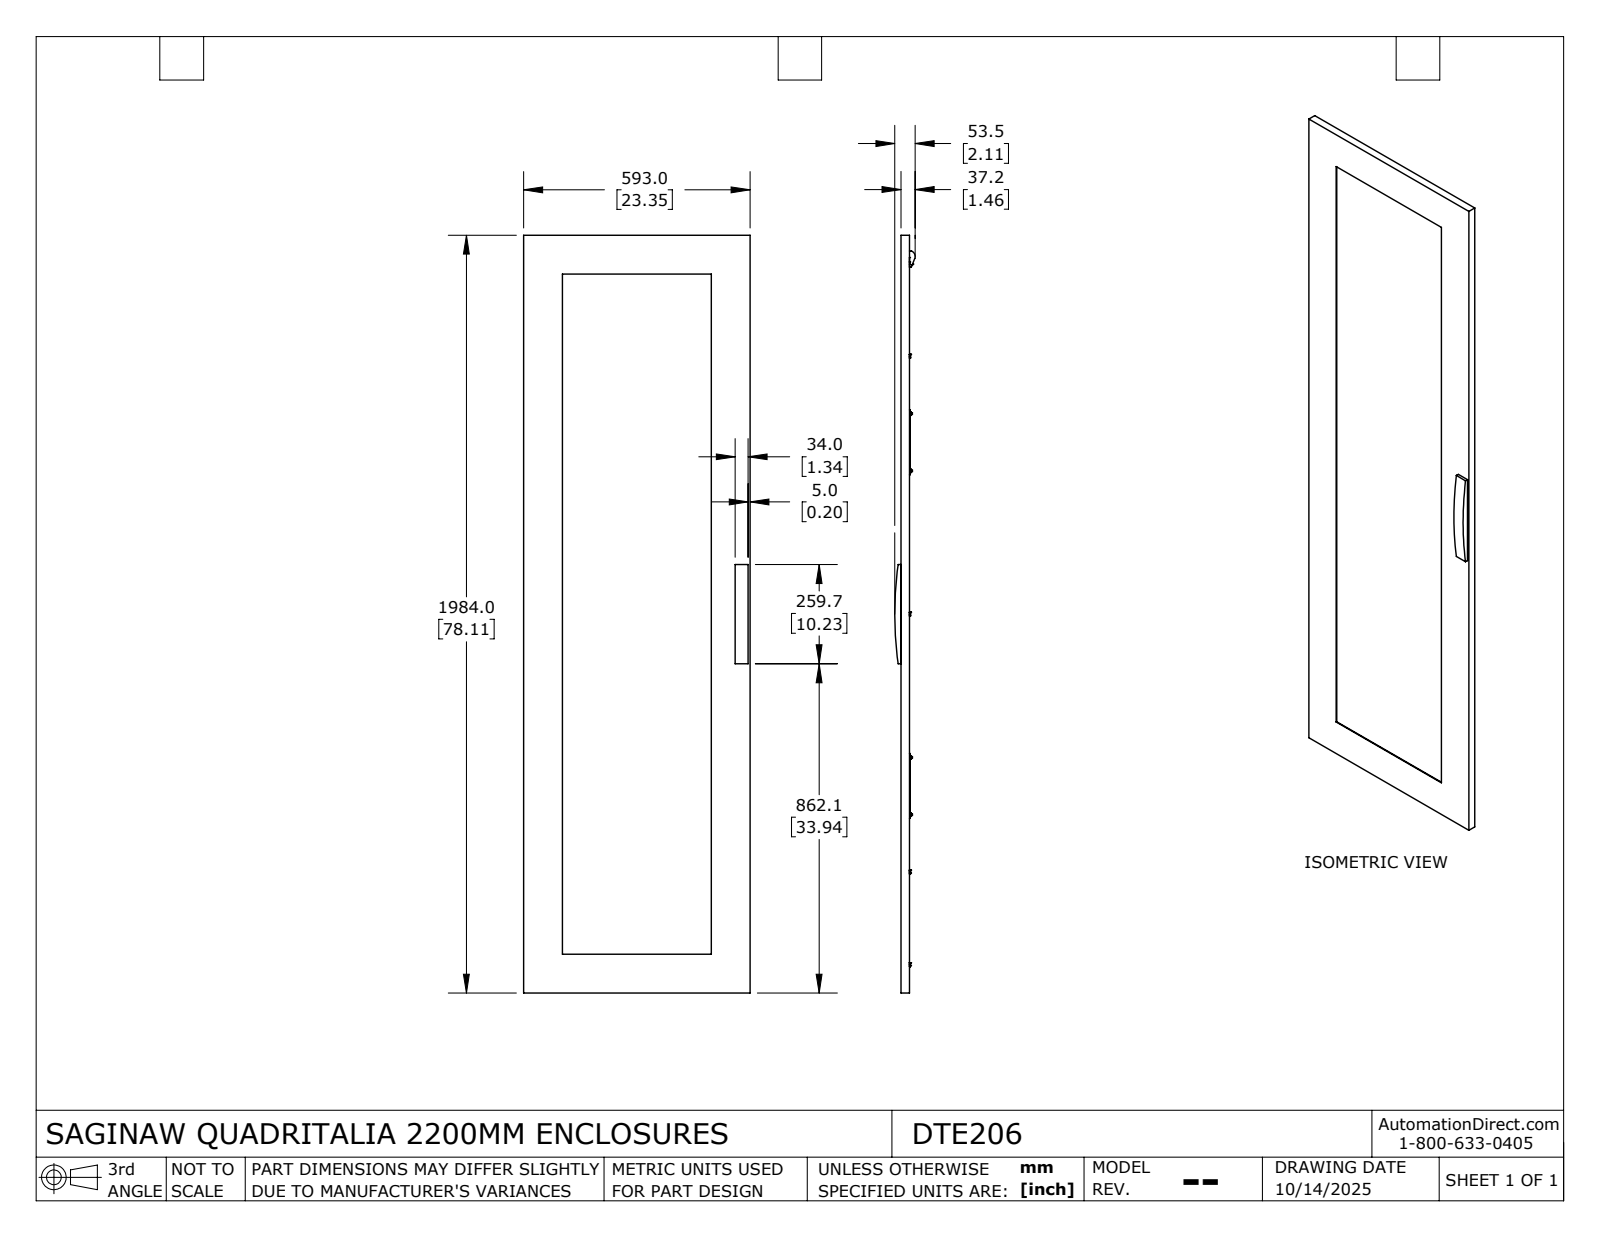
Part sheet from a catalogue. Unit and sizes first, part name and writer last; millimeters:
Units: millimetres
Overall size (bounding box): 1984 × 593 × 53.48
Round holes (diameter × count): ⌀4.25 ×128, ⌀7.99 ×28, ⌀8.99 ×14, ⌀4.91 ×10, ⌀8.99 ×4, ⌀4.5 ×2
Round bosses / shafts (diameter × count): ⌀7.19 ×10, ⌀5.99 ×10, ⌀9.99 ×8, ⌀6.99 ×8, ⌀5 ×5, ⌀4.99 ×4, ⌀6.99 ×2
Partial cylindrical surfaces — rounded edges, fillets, slot ends (radius × count): R5.77 ×10, R2.12 ×8, R7.51 ×4, R6 ×2, R15.08 ×1, R961.9 ×1
Main face-to-face distances: 4, 2, 6, 19.98, 19.99, 21.99, 2.01, 15.99, 3.99, 591
Hole centre spacings: 460.66, 49.95, 462.68, 466.04, 459.98, 24.97, 24.98, 99.9
Volume: 6 723 000 mm³ · Surface area: 3 431 000 mm²
Bodies: 11 solids, 1026 faces (557 planar, 307 cylindrical, 162 other)
Part name (STEP PRODUCT): DTE206; DTE206_Default
STEP written by: SolidWorks 2024 (CONFIG_CONTROL_DESIGN)
